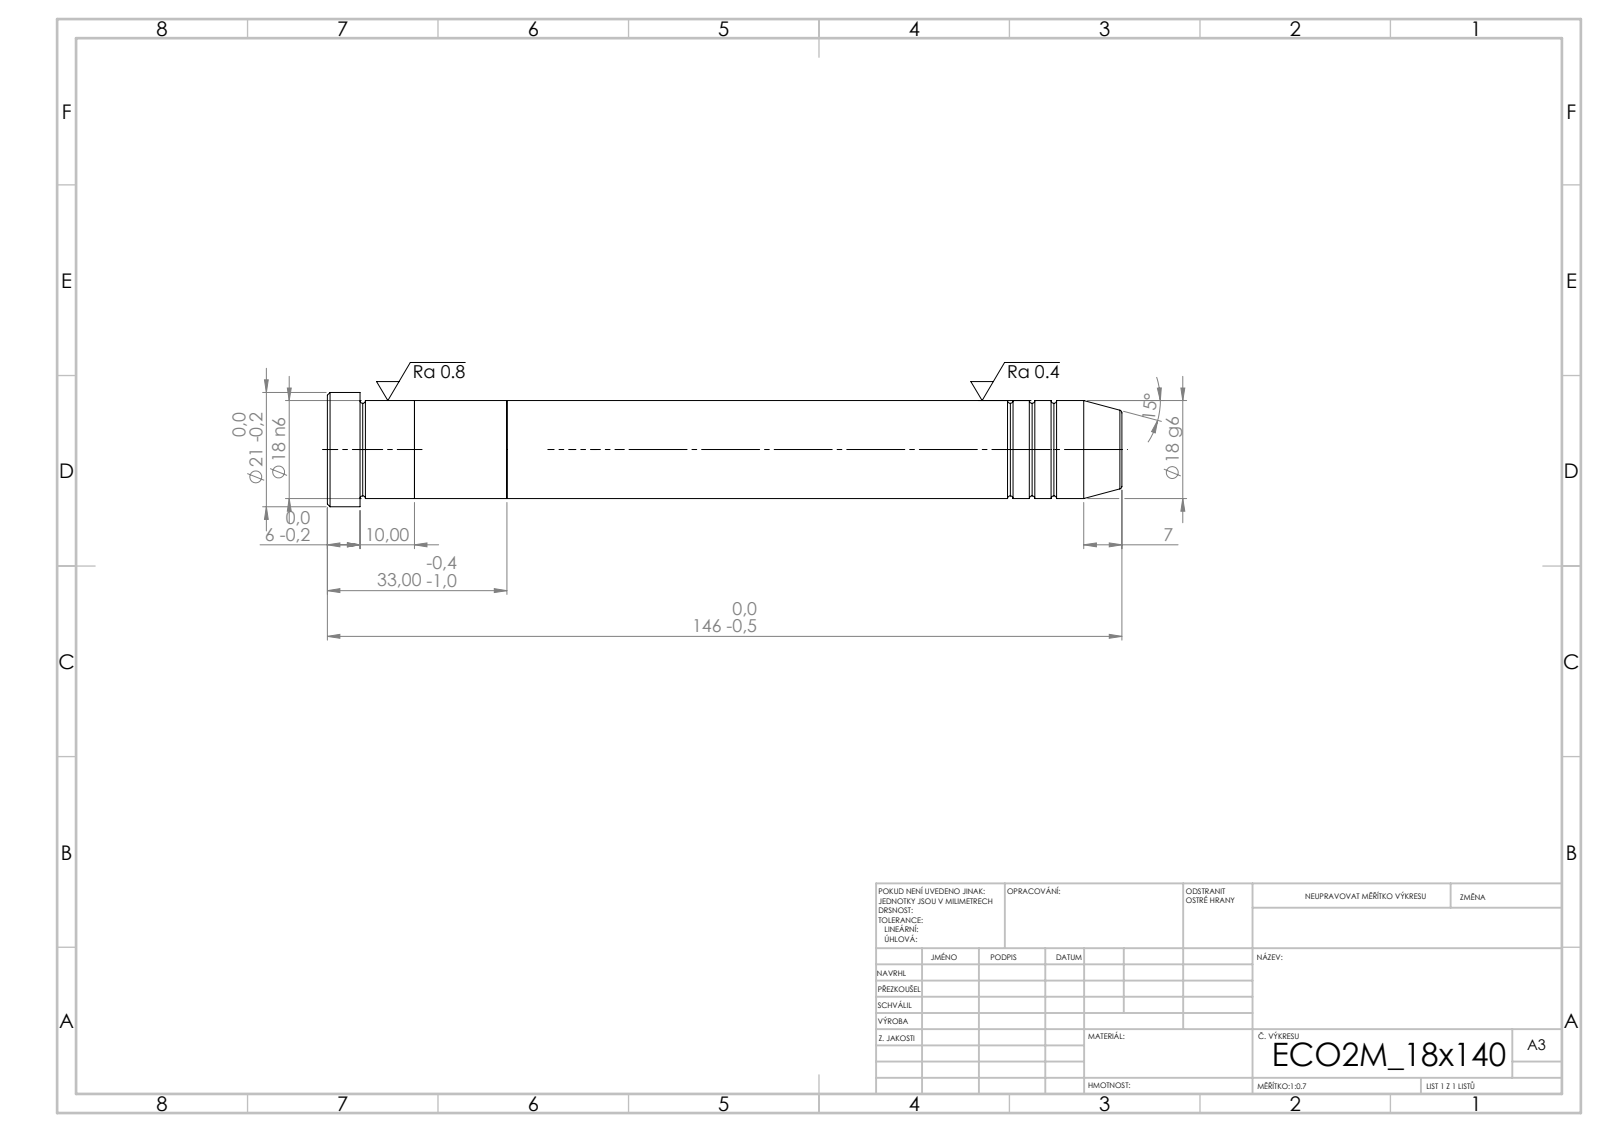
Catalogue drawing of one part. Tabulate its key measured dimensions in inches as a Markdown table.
| quantity | value |
| --- | --- |
| STEP written by | SolidWorks 2019 (CONFIG_CONTROL_DESIGN) |
| units | inches |
| bodies | 3 solids, 43 faces (7 planar, 14 cylindrical, 22 other) |
| overall size | 5.748 × 0.827 × 0.827 |
| volume | 2.274 in³ |
| surface area | 15.49 in² |
| round bosses / shafts (diameter × count) | 0.827 × 1, 0.709 × 1 |
| main face-to-face distances | 0.669, 1.299, 0.63, 4.449, 5.118, 5.748, 5.512, 1.063, 0.394, 0.236 |
